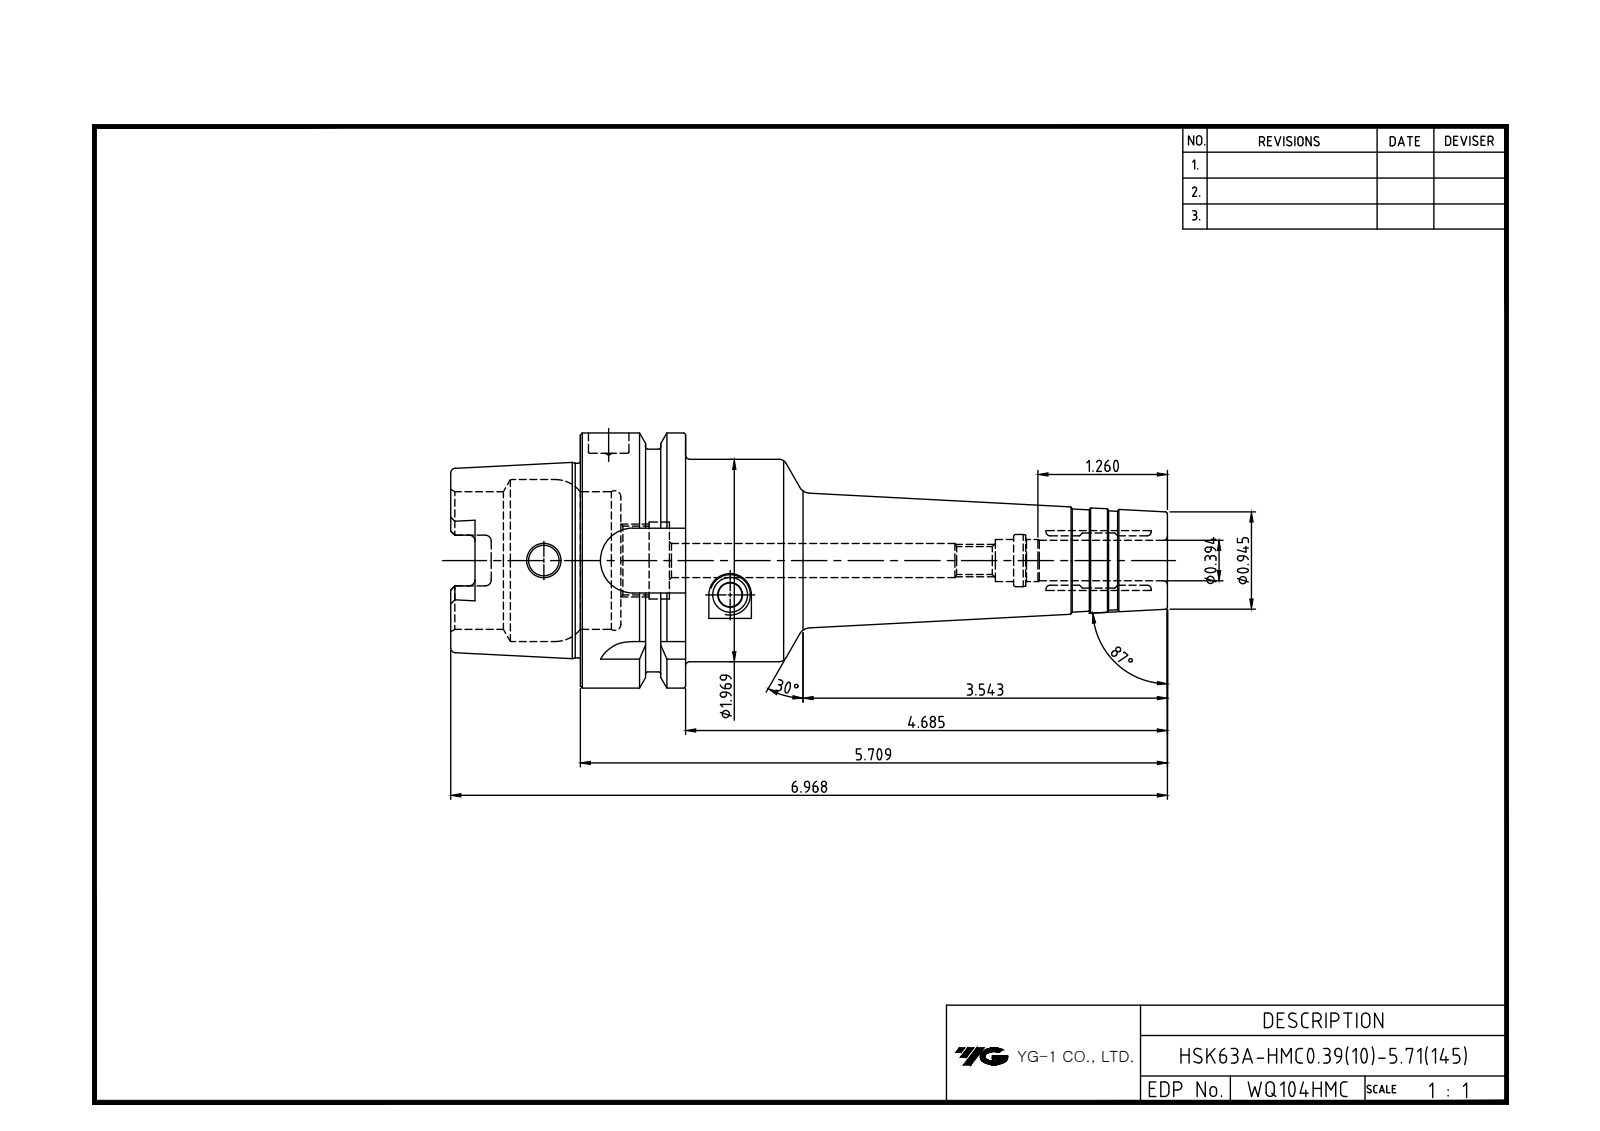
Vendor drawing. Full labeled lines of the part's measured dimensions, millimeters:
Part name (STEP PRODUCT): LO-HSK63A-HMC10-145
STEP written by: Autodesk Inventor 2020 (AUTOMOTIVE_DESIGN)
Units: millimetres
Bodies: 1 solid, 136 faces (42 planar, 34 cylindrical, 60 other)
Overall size (bounding box): 177 × 63 × 63
Volume: 187 149 mm³ · Surface area: 37 132 mm²
Round holes (diameter × count): ⌀10 ×2, ⌀6.92 ×1, ⌀7.5 ×1, ⌀8 ×1, ⌀10.6 ×1, ⌀16.92 ×1, ⌀19 ×1, ⌀34 ×1, ⌀40 ×1
Round bosses / shafts (diameter × count): ⌀63 ×1, ⌀55 ×1, ⌀50 ×1, ⌀48.04 ×1
Partial cylindrical surfaces — rounded edges, fillets, slot ends (radius × count): R1.5 ×6, R2.88 ×4, R8 ×4
Main face-to-face distances: 26, 10, 16, 32, 42, 58, 177, 145, 135, 119
